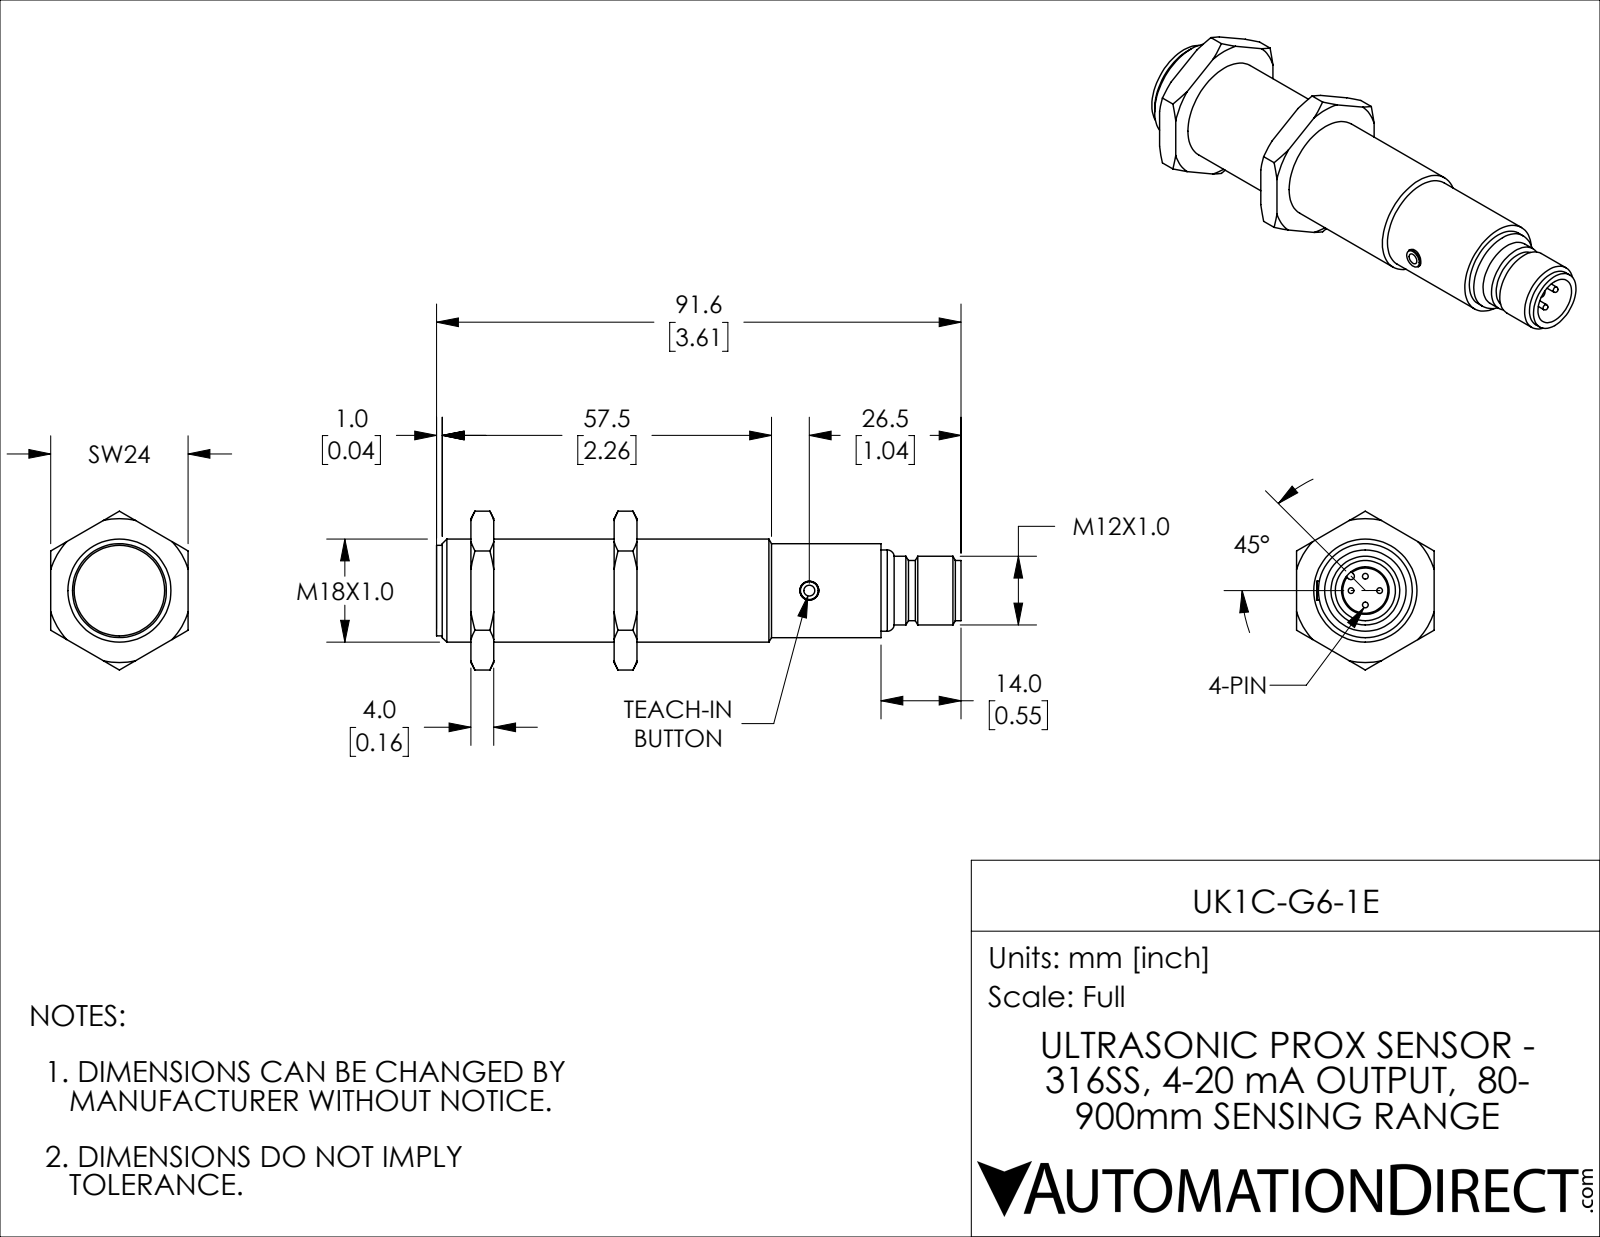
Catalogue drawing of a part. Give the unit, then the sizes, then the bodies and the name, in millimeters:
Units: millimetres
Overall size (bounding box): 91.6 × 27.7 × 24
Round holes (diameter × count): ⌀3.3 ×1, ⌀8.3 ×1, ⌀18 ×1
Round bosses / shafts (diameter × count): ⌀1 ×4, ⌀16.4 ×1, ⌀15.8 ×1, ⌀14.2 ×1, ⌀12 ×1, ⌀10.5 ×1
Partial cylindrical surfaces — rounded edges, fillets, slot ends (radius × count): R0.6 ×1
Main face-to-face distances: 25, 4, 24, 29, 21, 6, 10, 31, 35, 77.6
Volume: 21 930 mm³ · Surface area: 7 723 mm²
Bodies: 4 solids, 113 faces (27 planar, 35 cylindrical, 51 other)
Part name (STEP PRODUCT): UK1C-G6-1E
STEP written by: SolidWorks 2018 (AUTOMOTIVE_DESIGN)
